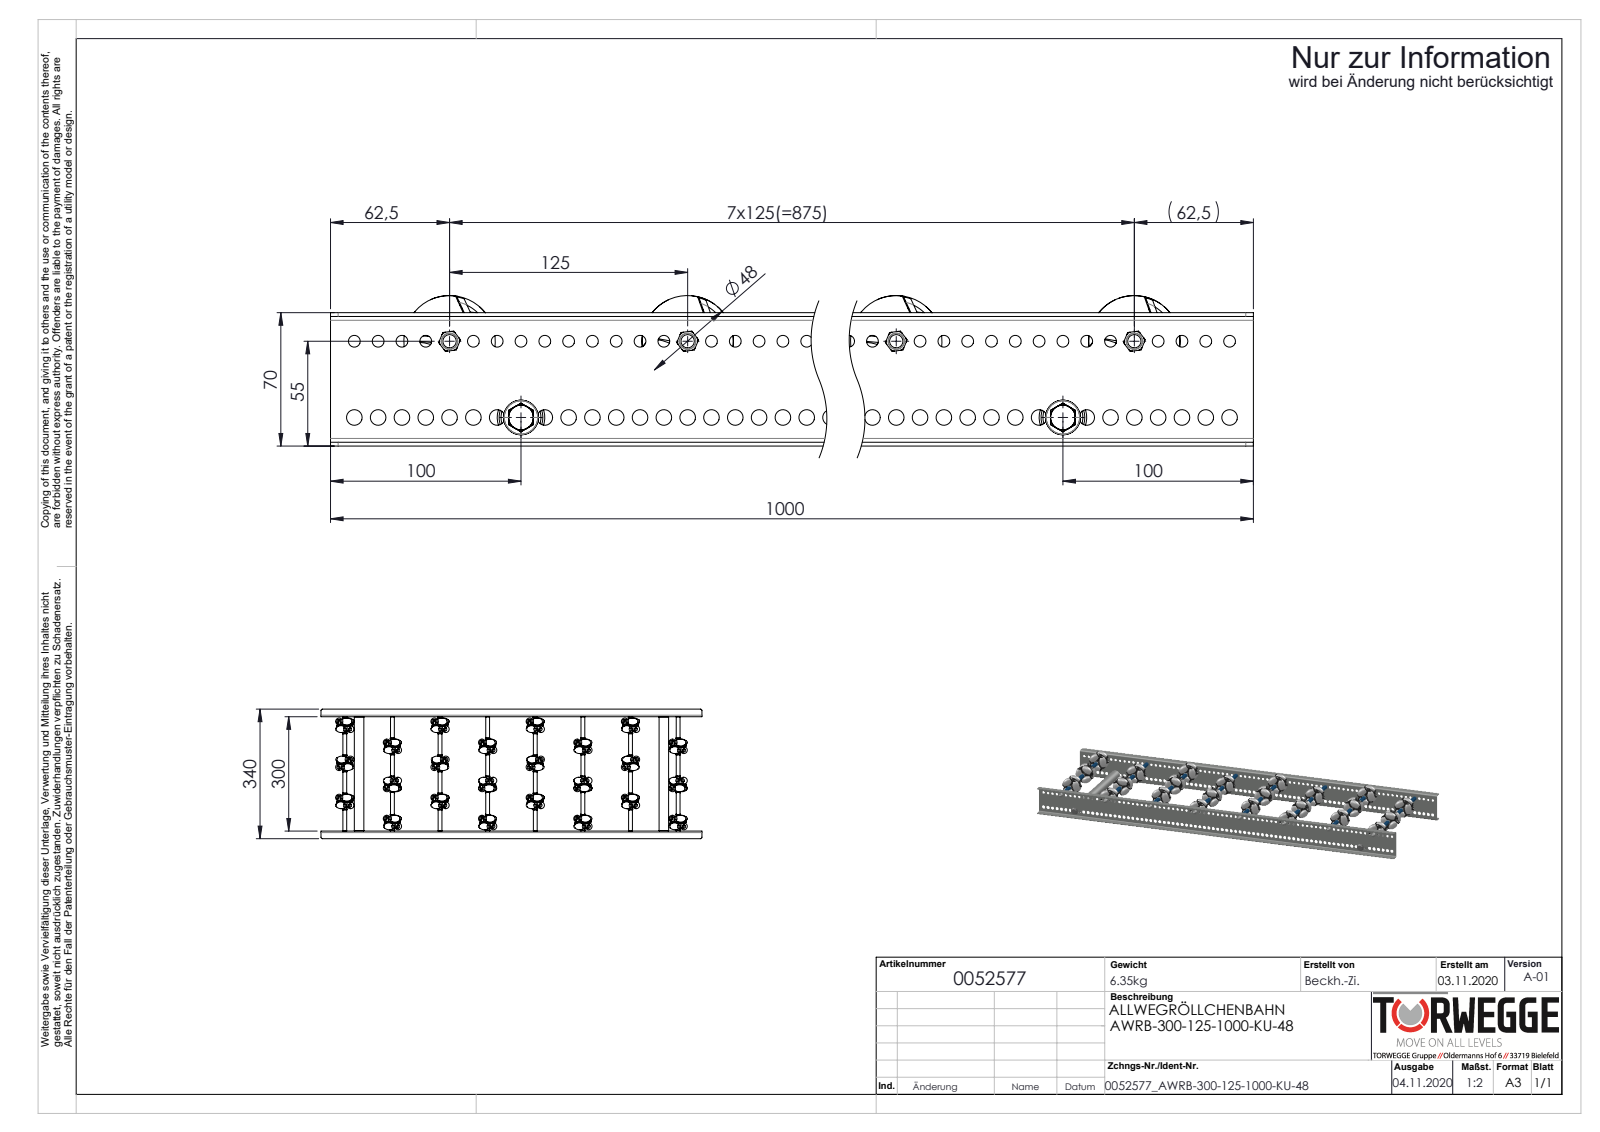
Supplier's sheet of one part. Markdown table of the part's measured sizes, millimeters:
| quantity | value |
| --- | --- |
| part name | AWR48_Röllchen; AWR48_Halter; 0019719_Gewindestange-M6_L=320; Profil-RB-20x70x20x2_S100215_U-PROFIL-20-70-20-2-RB-L=1000 (+8 more) |
| STEP written by | SolidWorks 2020 (AUTOMOTIVE_DESIGN) |
| units | millimeters |
| bodies | 420 solids, 7968 faces (2616 planar, 3264 cylindrical, 2088 other) |
| overall size | 1000 × 340 × 78.99 |
| volume | 1 660 000 mm³ |
| surface area | 1 240 000 mm² |
| round holes (diameter × count) | 3.7 × 144, 4.2 × 144, 6.2 × 79, 8.2 × 79, 4.92 × 8, 6.5 × 8, 8.4 × 8, 6.8 × 2, 21 × 2 |
| round bosses / shafts (diameter × count) | 4 × 144, 3.7 × 118, 8 × 10, 42 × 8, 11 × 8, 10 × 8, 7 × 8, 6 × 8 |
| partial cylindrical surfaces (radius × count) | 4 × 8, 23.55 × 8, 2 × 4 |
| main face-to-face distances | 2, 302, 68, 300, 304, 66, 70, 3, 11.75, 20 |
| hole center spacings | 36.05, 36.06, 125, 36.07, 250, 12.5, 25, 36.04 |
